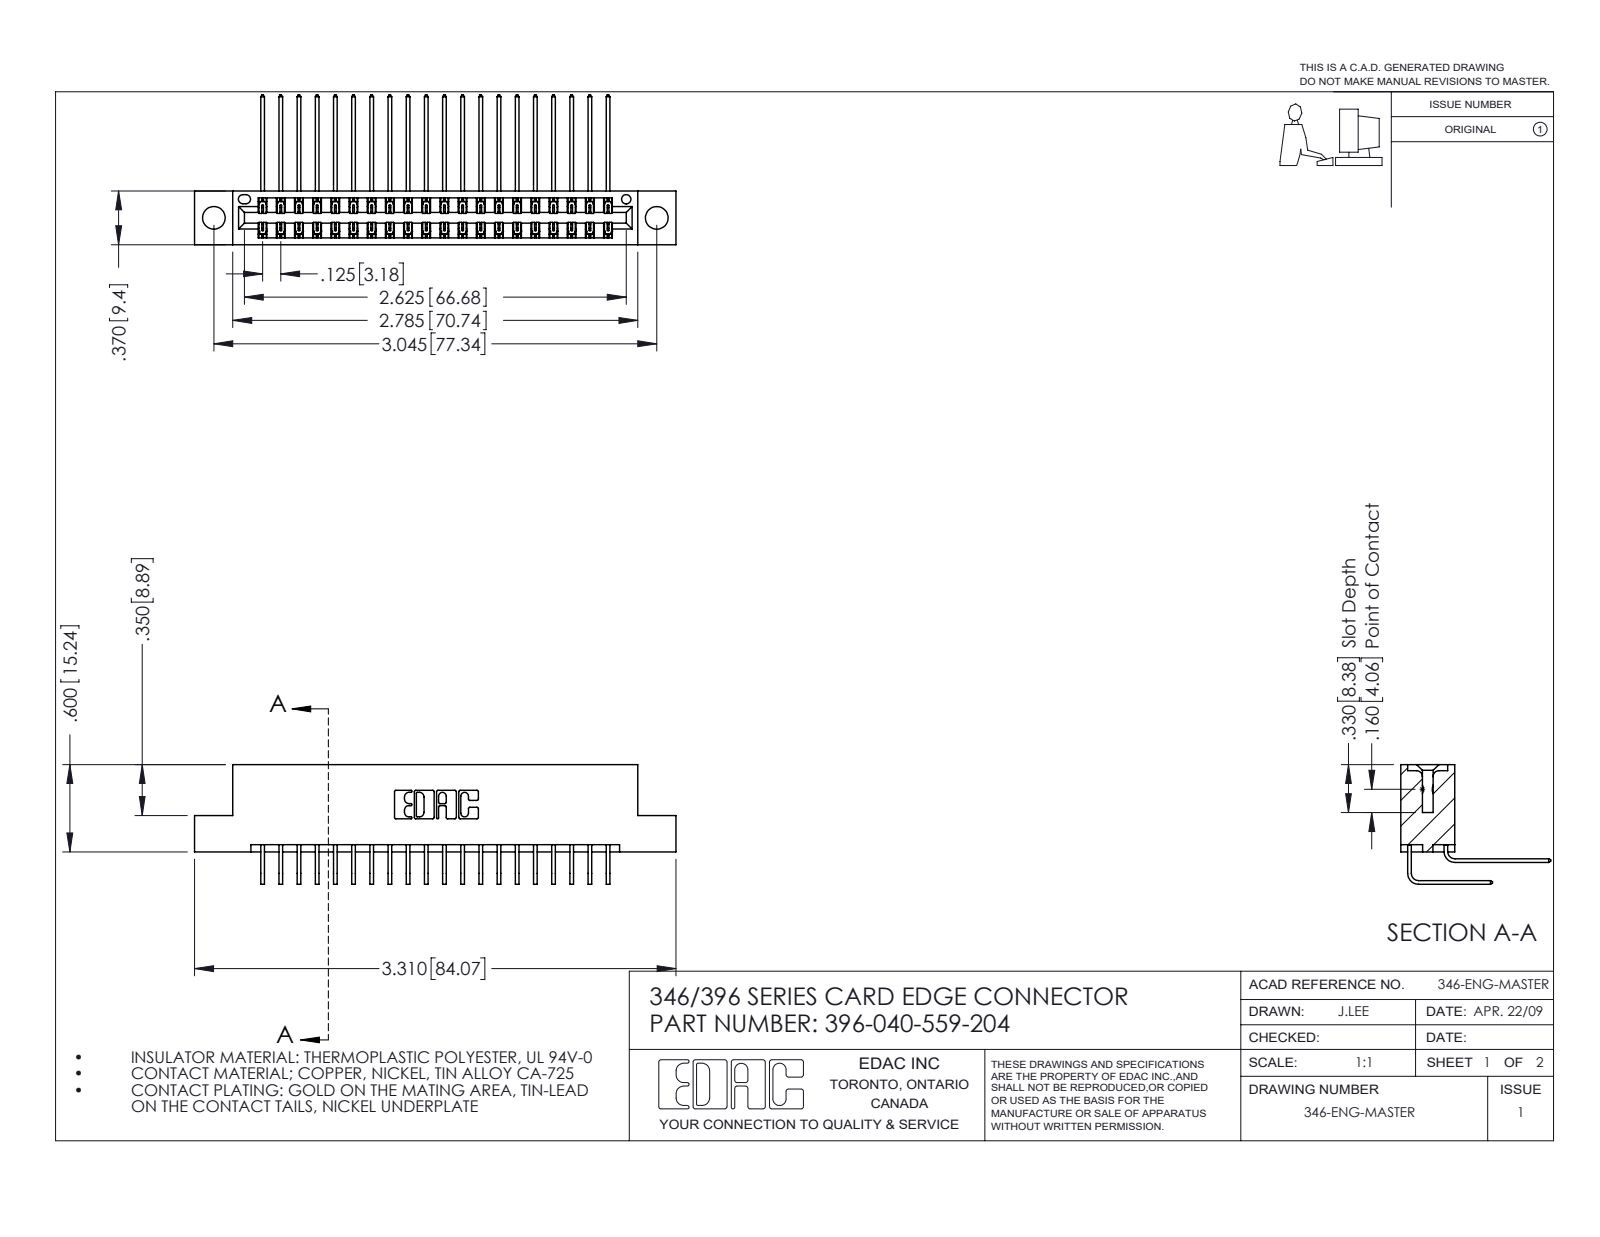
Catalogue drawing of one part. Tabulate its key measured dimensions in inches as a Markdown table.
| quantity | value |
| --- | --- |
| part name | 345-292-001_559 Tail - 2; 396-040-559-204; 346 Part_Flush Mounting Lugs - 0.156 Dia-TH; 345-292-001_558 559 Tail - 1 |
| STEP written by | SolidWorks 2016 (CONFIG_CONTROL_DESIGN) |
| units | inches |
| bodies | 41 solids, 2282 faces (1556 planar, 726 cylindrical, 0 other) |
| overall size | 3.31 × 1.03 × 0.823 |
| volume | 0.499 in³ |
| surface area | 18.3 in² |
| round holes (diameter × count) | 0.156 × 2, 0.064 × 1 |
| partial cylindrical surfaces (radius × count) | 0.006 × 60, 0.01 × 22, 0.007 × 6, 0.031 × 6, 0.026 × 3, 0.014 × 2, 0.022 × 2, 0.024 × 2 |
| main face-to-face distances | 0.048, 0.322, 0.25, 0.025, 0.37, 0.072, 0.298, 0.275, 0.148, 0.222 |
| hole center spacings | 0.246, 2.837, 3.045 |
